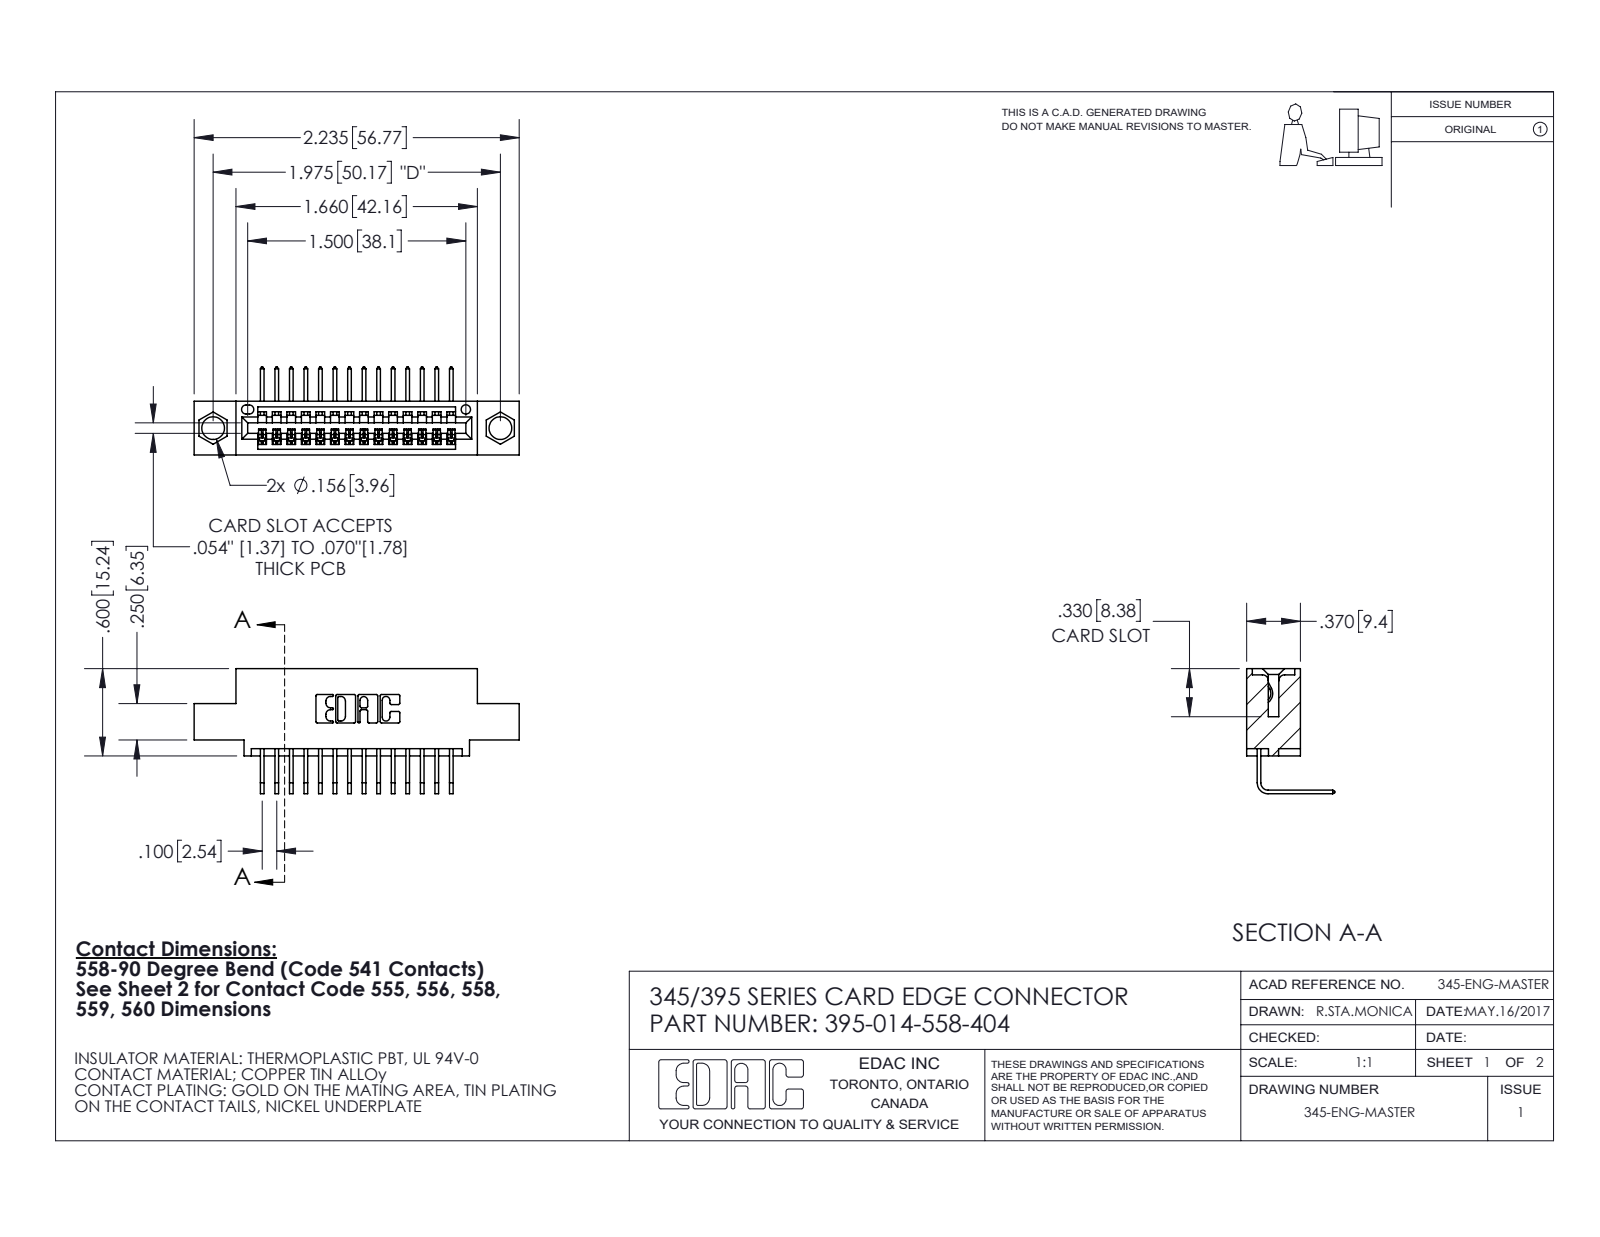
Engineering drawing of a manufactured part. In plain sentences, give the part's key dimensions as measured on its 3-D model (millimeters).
The part is named "345-292-001_558 Tail - 2; 345 Part_0.110 Offset - 0.156 Dia-TI; 395-014-558-404". Its 3-D file was written by "SolidWorks 2020 (CONFIG_CONTROL_DESIGN)". It is 15 solids with 984 faces: 686 planar, 298 cylindrical and 0 other. Overall it measures 56.8 by 21.8 by 15.4 millimeters. Its volume is 5 030 cubic millimeters and its surface area 6 503 square millimeters. Round holes: 2 of diameter 4, 1 of diameter 1.6. Partial cylindrical surfaces (rounded edges, fillets, slot ends): 28 of radius 0.2, 22 of radius 0.3, 6 of radius 0.2, 6 of radius 0.8, 3 of radius 0.7, 2 of radius 0.8, 2 of radius 1, 1 of radius 0.4. The main face-to-face distances are 1.8, 7.6, 5.1, 9.4, 2.5, 6.9, 0.6, 5.7, 2.5, 7.6. The hole center spacings are 6.9, 44.2, 50.2.
